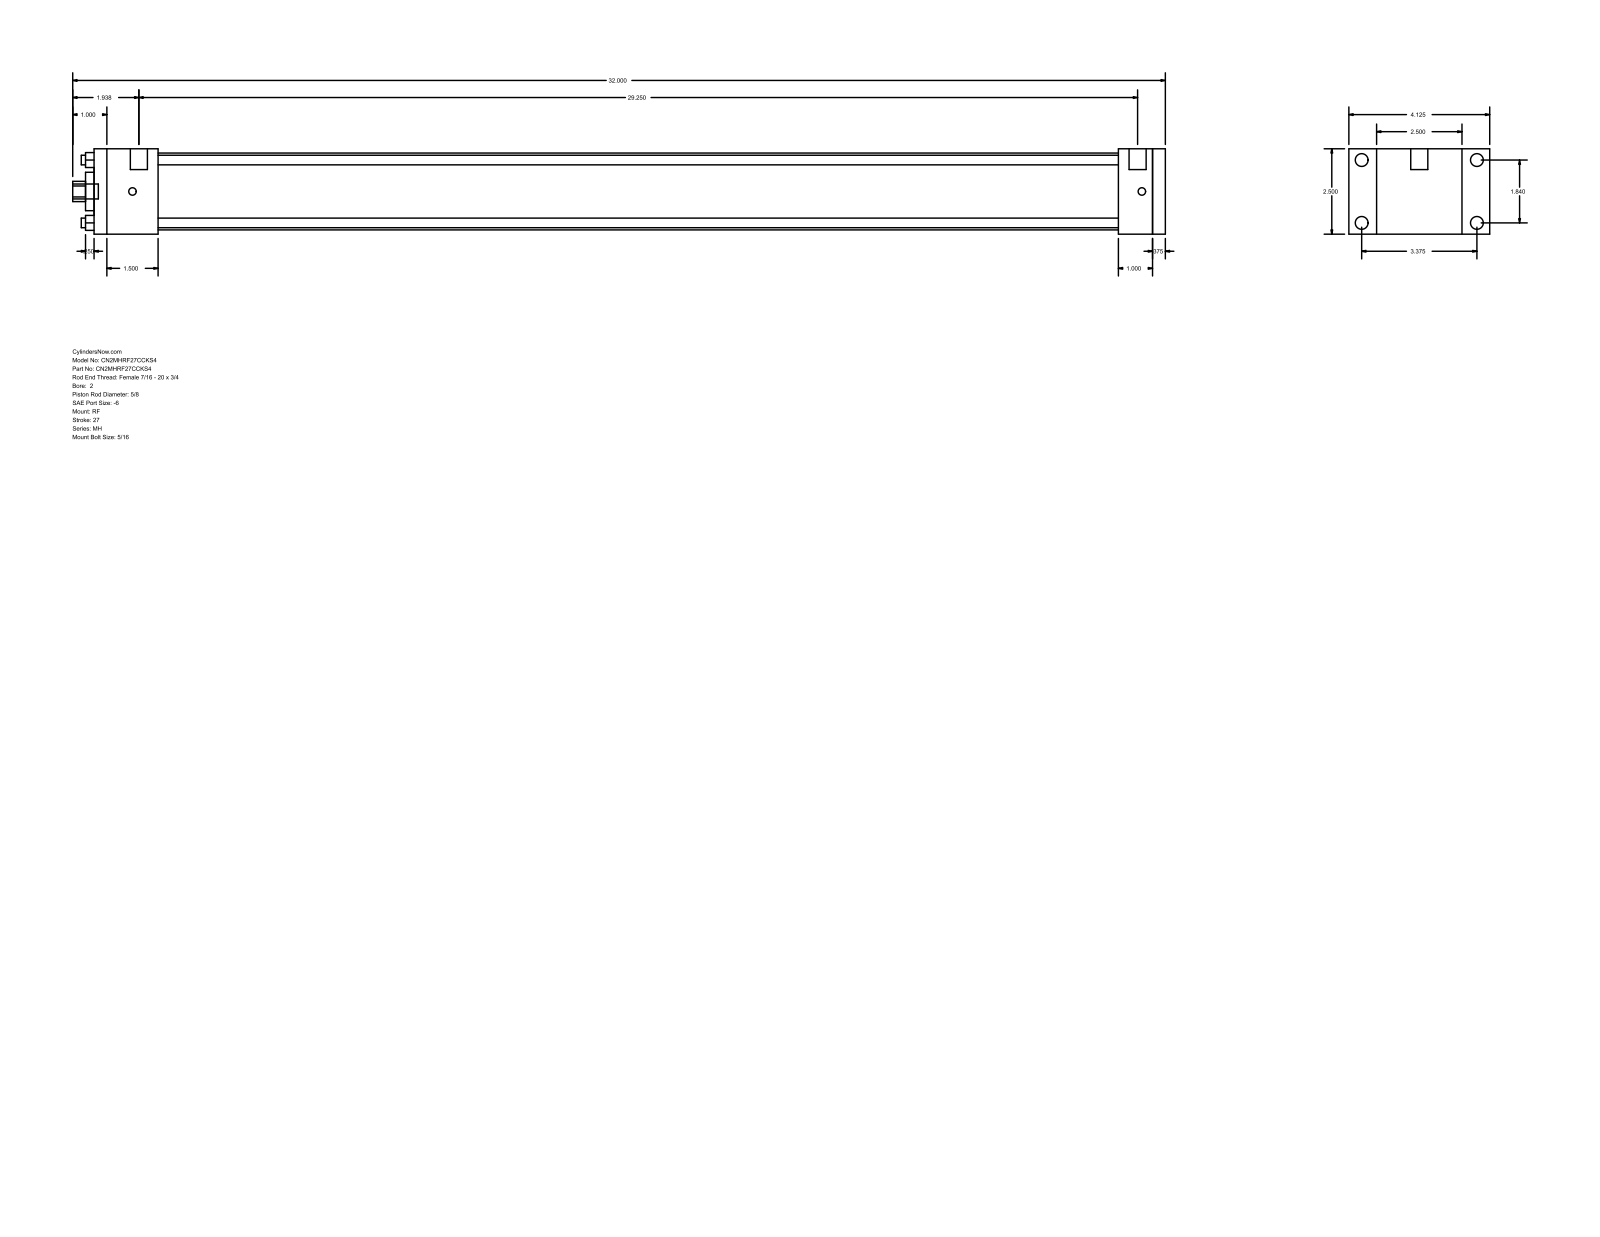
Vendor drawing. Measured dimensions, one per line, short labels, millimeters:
name: MH_RF__0200_0.625
written by: GSSL Pune (CONFIG_CONTROL_DESIGN)
unit: mm
bodies: 0 solids, 92 faces (64 planar, 28 cylindrical, 0 other)
size: 812.8 × 104.78 × 63.5
holes: 4× ⌀7.14, 1× ⌀15.88, 1× ⌀28.57, 1× ⌀57.15
bosses: 4× ⌀9.53, 4× ⌀5.56, 2× ⌀12.7, 1× ⌀11.11
rounds: 1× R7.54
face distances: 63.5, 796.92, 9.53, 787.39, 47.62, 762, 714.38, 739.77, 749.3, 25.39
hole spacings: 33.05, 46.74, 66.1
